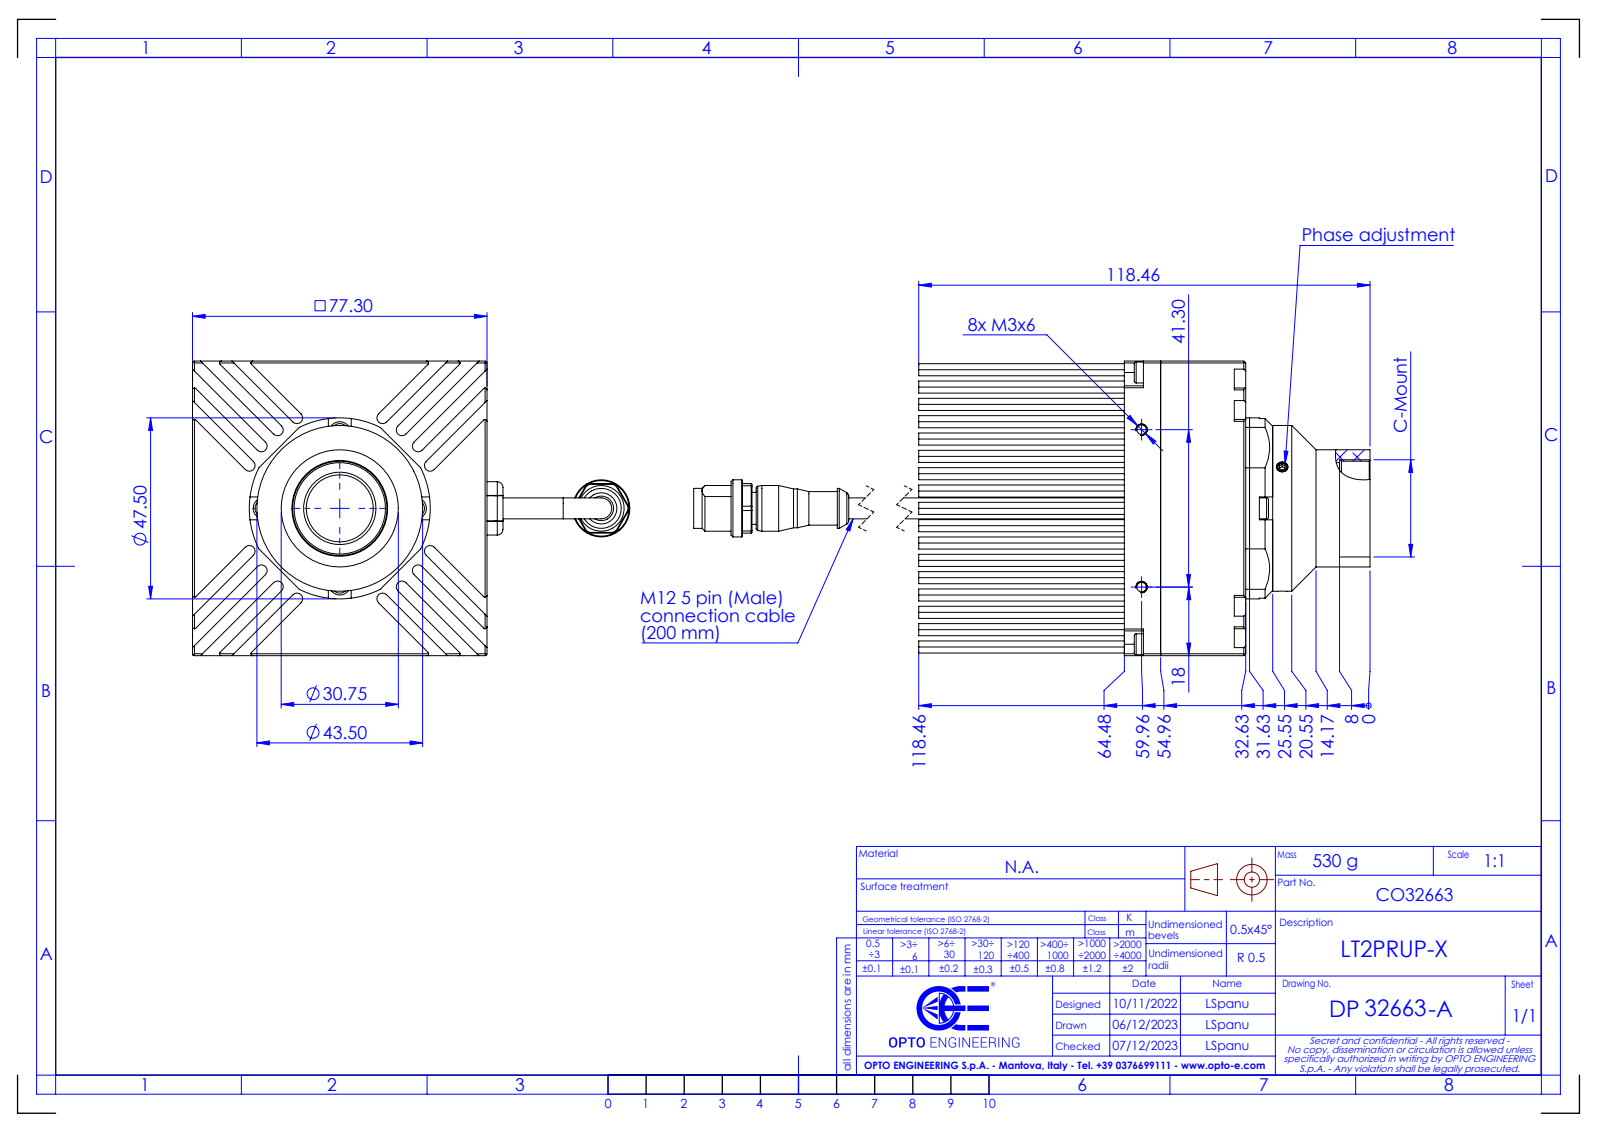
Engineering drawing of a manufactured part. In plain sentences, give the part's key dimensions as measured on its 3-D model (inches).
The part is named "DP32663-A_LT2PRUP-X". Its 3-D file was written by "SolidWorks 2021 (CONFIG_CONTROL_DESIGN)". It is 0 solids with 823 faces: 380 planar, 398 cylindrical and 45 other. Overall it measures 7.979 by 4.52 by 3.043 inches. Round holes: 7 of diameter 0.098, 1 of diameter 0.138, 1 of diameter 0.327, 1 of diameter 0.748, 1 of diameter 0.945, 1 of diameter 0.974, 1 of diameter 0.998. Round bosses or shafts: 99 of diameter 0.125, 42 of diameter 0.125, 10 of diameter 0.217, 5 of diameter 0.039, 1 of diameter 1.713, 1 of diameter 1.211, 1 of diameter 0.591, 1 of diameter 0.559. Partial cylindrical surfaces (rounded edges, fillets, slot ends): 28 of radius 0.02, 18 of radius 0.059, 4 of radius 0.138, 1 of radius 0.024, 1 of radius 0.283, 1 of radius 0.935. The main face-to-face distances are 3.043, 1.254, 0.118, 1.136, 2.125, 3.261, 3.38, 0.23, 0.465, 0.235. The hole center spacings are 1.626, 1.665, 0.545, 1.4, 2.703.
